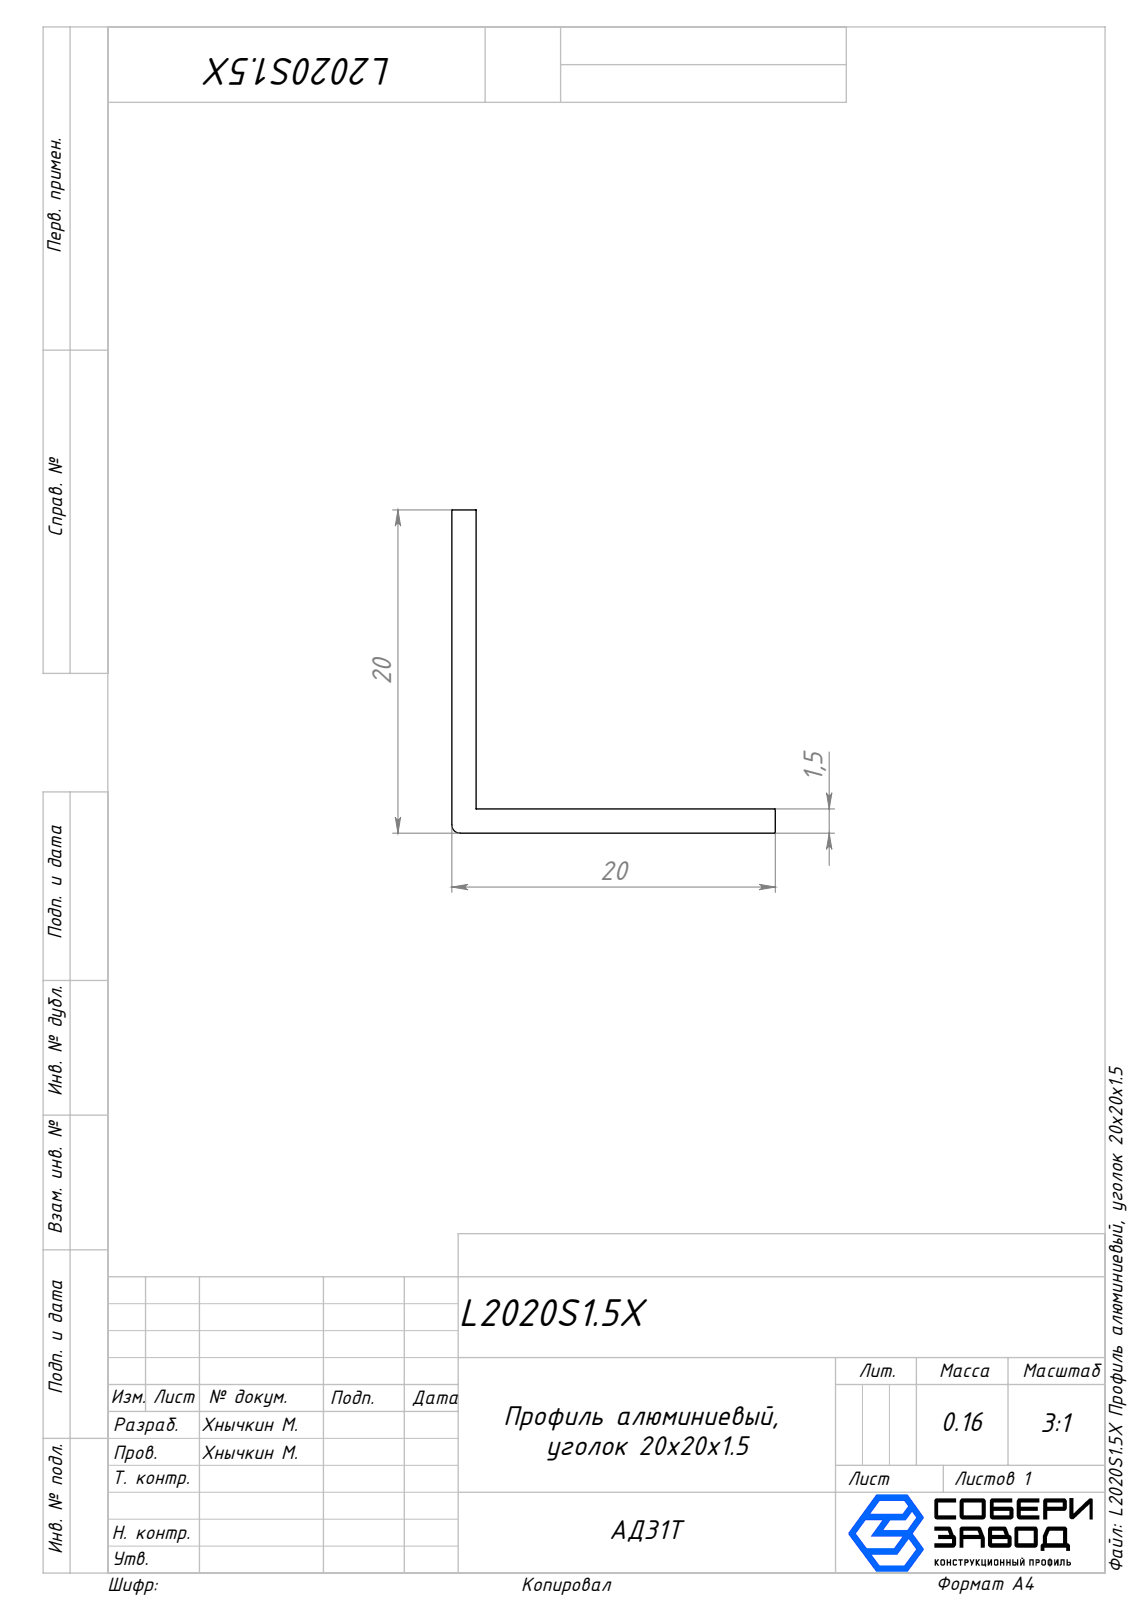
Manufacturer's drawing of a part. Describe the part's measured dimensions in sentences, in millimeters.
The part is named "L2020S1.5X Профиль алюминиевый, уголок 20х20х1.5". Its 3-D file was written by "SolidWorks 2025 (AUTOMOTIVE_DESIGN)". It is 1 solid with 9 faces: 8 planar, 1 cylindrical and 0 other. Overall it measures 1000 by 20 by 20 millimeters. Its volume is 57 696 cubic millimeters and its surface area 79 901 square millimeters. Partial cylindrical surfaces (rounded edges, fillets, slot ends): 1 of radius 0.5. The main face-to-face distances are 1.5, 20, 18.5, 1000.
